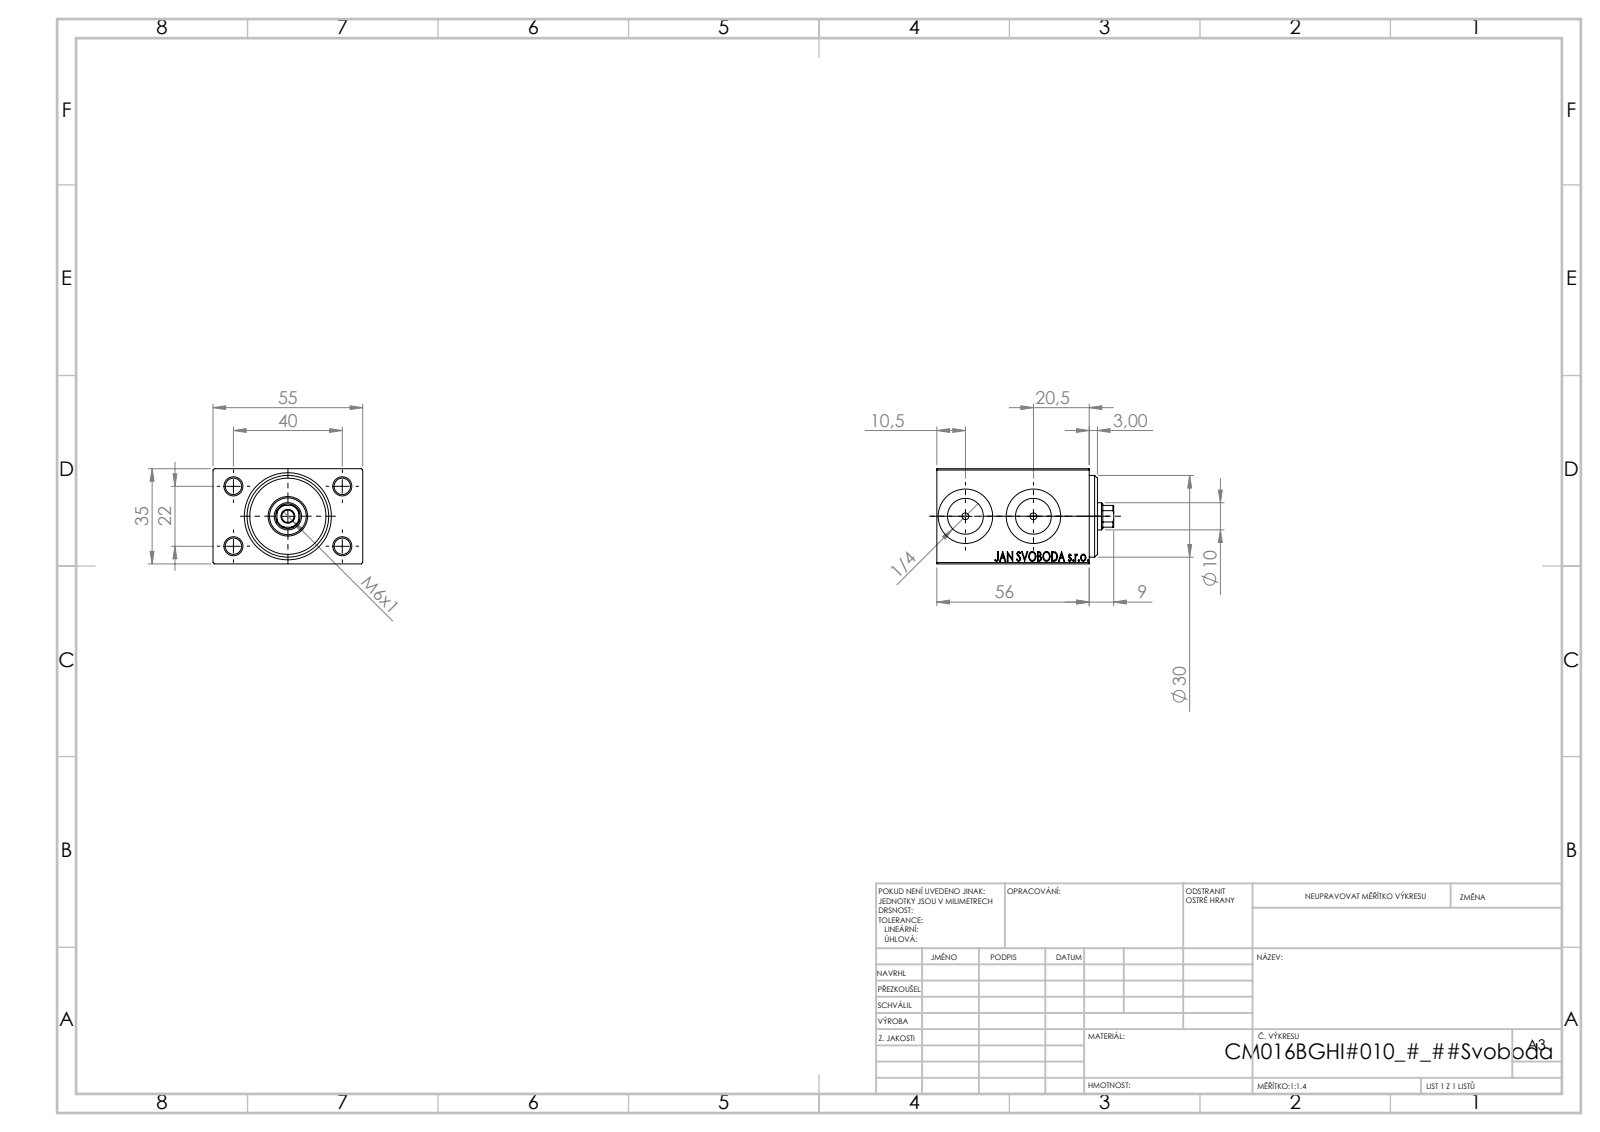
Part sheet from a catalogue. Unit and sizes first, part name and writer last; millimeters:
Units: millimetres
Overall size (bounding box): 65 × 55 × 35
Round holes (diameter × count): ⌀6 ×4, ⌀2.5 ×2, ⌀13.16 ×2, ⌀20 ×2, ⌀4.5 ×1, ⌀10 ×1, ⌀13.5 ×1, ⌀14.5 ×1, ⌀16 ×1, ⌀18 ×1, ⌀30 ×1
Partial cylindrical surfaces — rounded edges, fillets, slot ends (radius × count): R4.5 ×1
Main face-to-face distances: 35, 5, 51, 55, 56, 42, 8, 3, 59, 54
Hole centre spacings: 22.83, 22, 40, 45.65, 25
Volume: 102 591 mm³ · Surface area: 25 030 mm²
Bodies: 3 solids, 881 faces (401 planar, 54 cylindrical, 426 other)
Part name (STEP PRODUCT): V450CM_B_Body; V450CM_B_VCP; V450CM_VC_B
STEP written by: SolidWorks 2019 (CONFIG_CONTROL_DESIGN)
